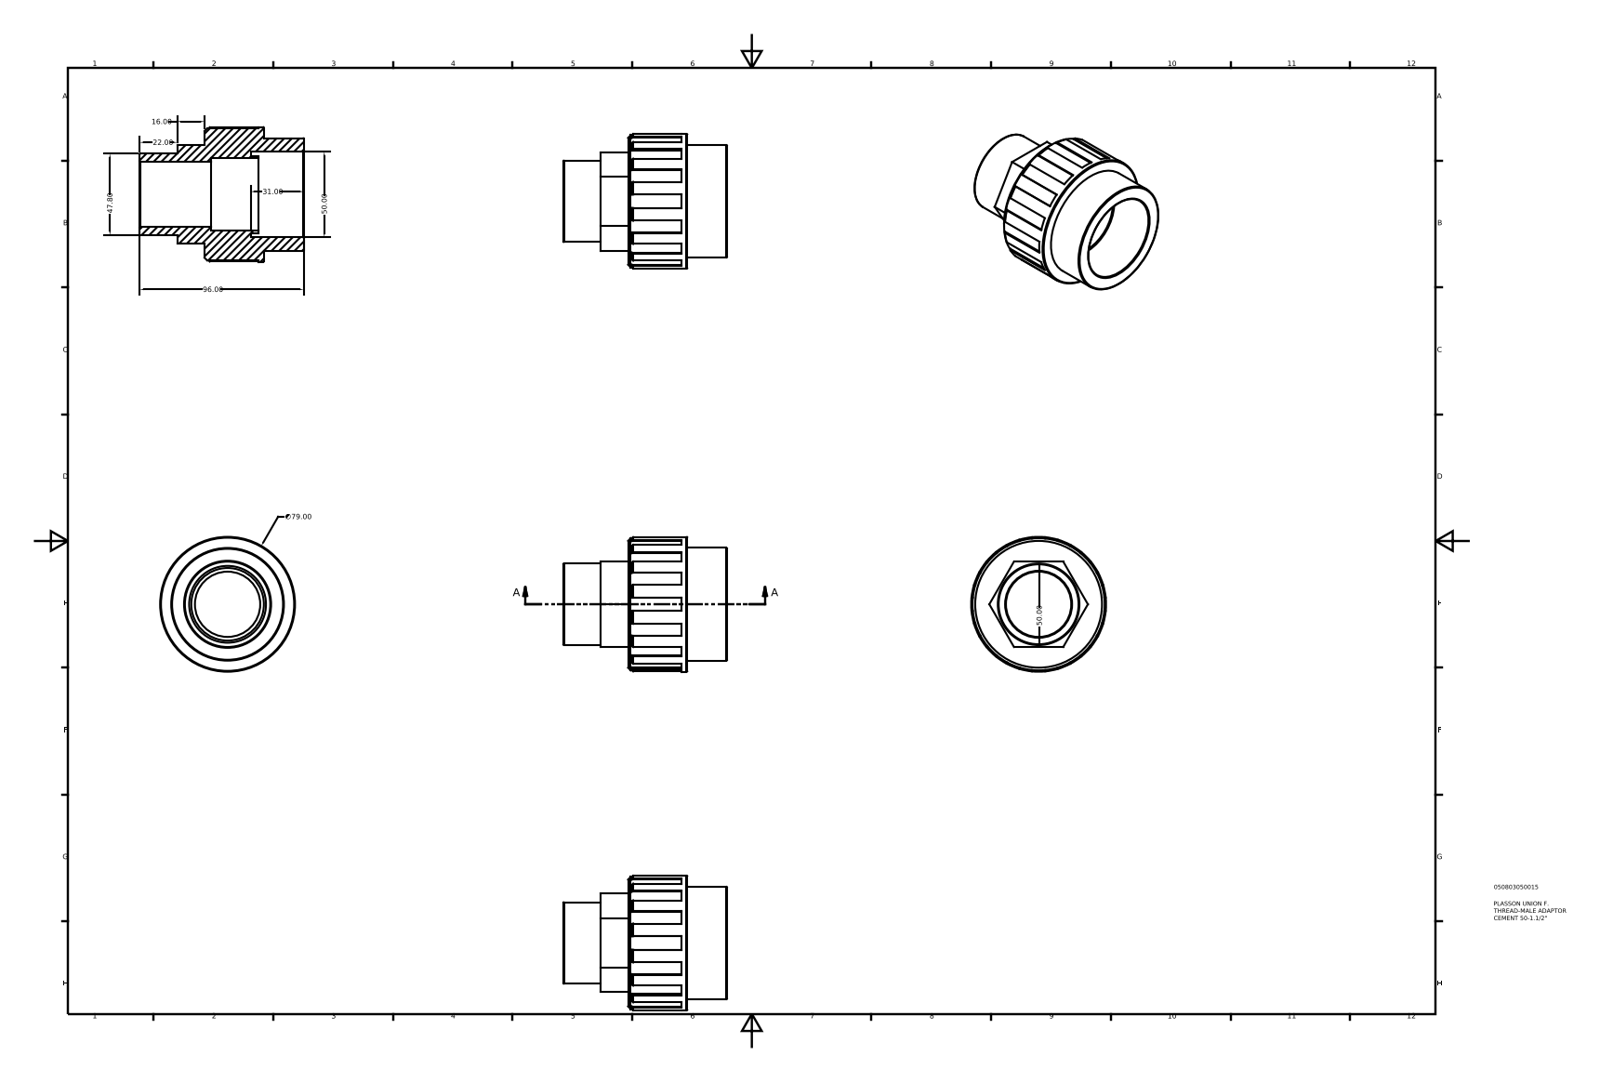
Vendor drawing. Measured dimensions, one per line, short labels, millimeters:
name: 050803050015
written by: Autodesk Inventor 2015 (AUTOMOTIVE_DESIGN)
unit: mm
bodies: 1 solid, 92 faces (62 planar, 8 cylindrical, 22 other)
size: 96 × 79 × 79
volume: 179 286 mm³; area: 41 451 mm²
holes: 1× ⌀38.24, 1× ⌀42.5, 1× ⌀50
bosses: 1× ⌀79, 1× ⌀77.42, 1× ⌀66, 1× ⌀47.8, 1× ⌀45
face distances: 50, 34.75, 58, 23.25, 38, 72.75, 96, 65, 27, 7.75
